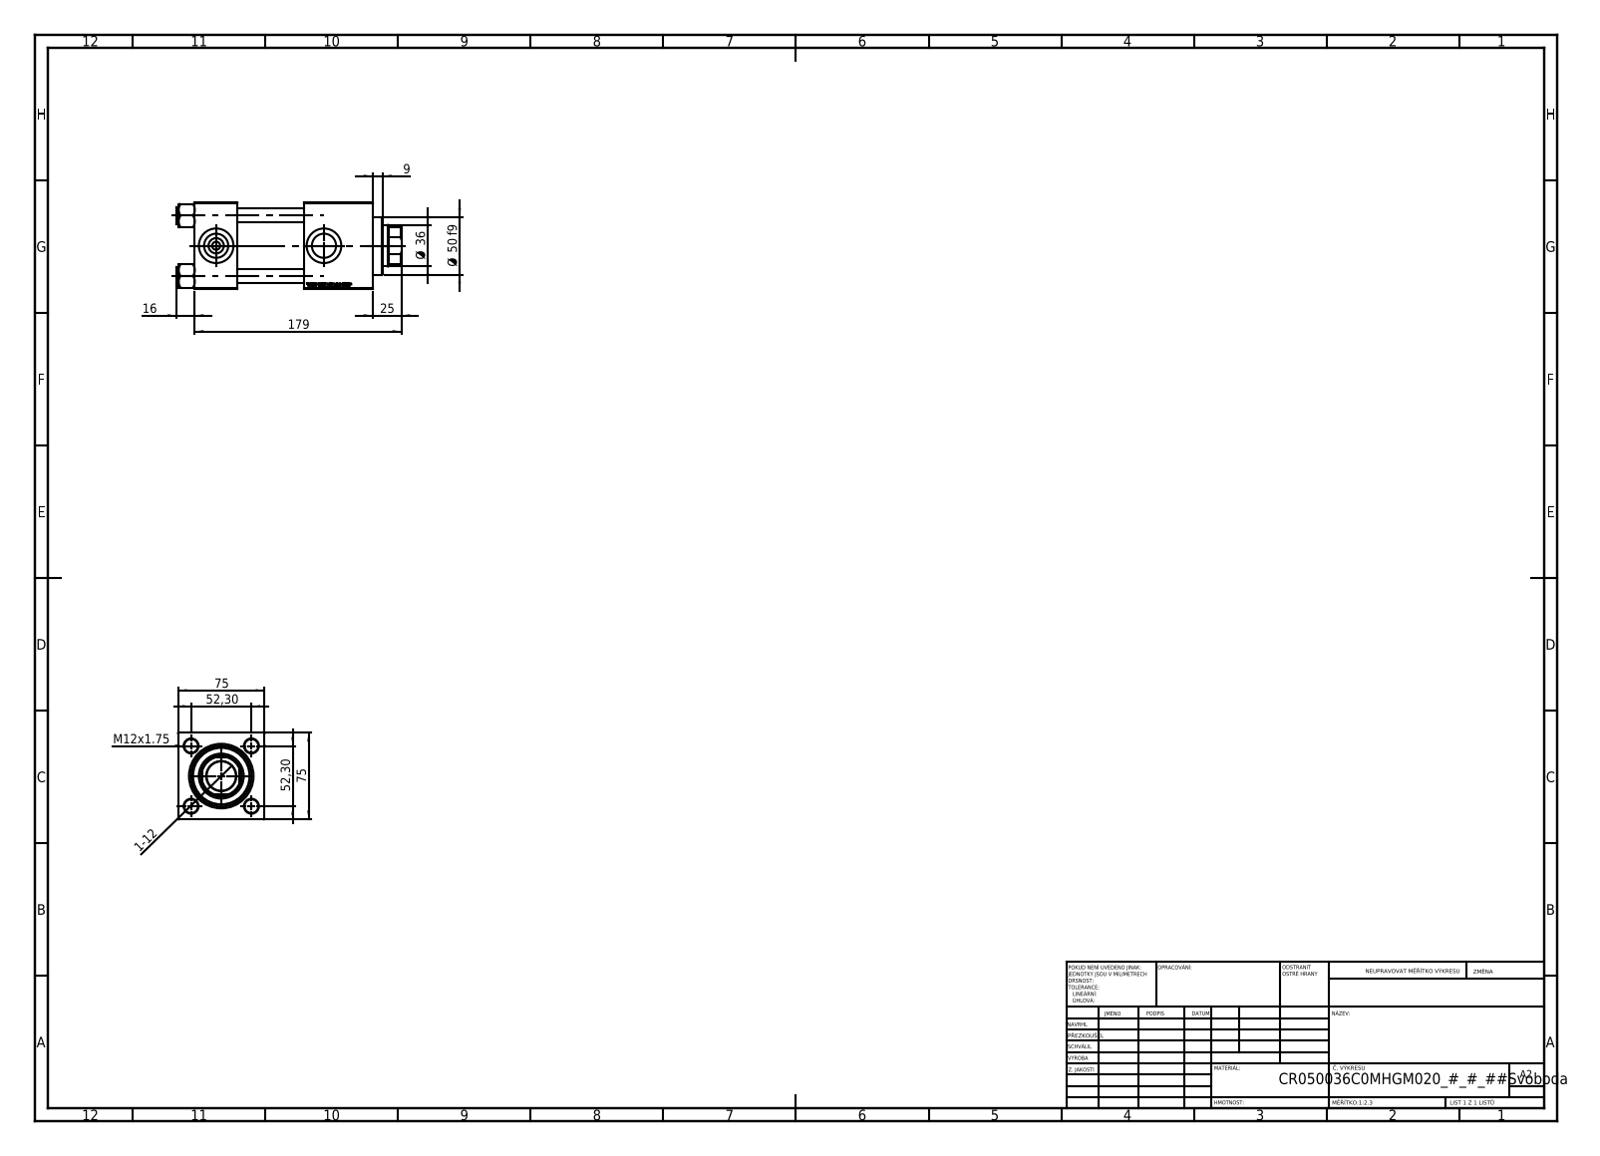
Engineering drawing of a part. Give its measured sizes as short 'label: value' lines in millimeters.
name: V215CR_C_TYCINKA; V215CR_VCP_C; V215CR_C_Body; V215_VC_A (+1 more)
written by: SolidWorks 2019 (CONFIG_CONTROL_DESIGN)
unit: mm
bodies: 11 solids, 1148 faces (526 planar, 86 cylindrical, 536 other)
size: 195 × 75.54 × 75
volume: 686 044 mm³; area: 155 490 mm²
holes: 4× ⌀12, 2× ⌀7, 2× ⌀20.96, 2× ⌀30, 1× ⌀25.5, 1× ⌀36, 1× ⌀39, 1× ⌀41, 1× ⌀53
bosses: 4× ⌀15, 1× ⌀56, 1× ⌀50
rounds: 1× R17.5
face distances: 75, 37, 95, 58, 154, 117, 59, 125.3, 88.3, 30.3
hole spacings: 36.98, 52.3, 73.96, 93.5
